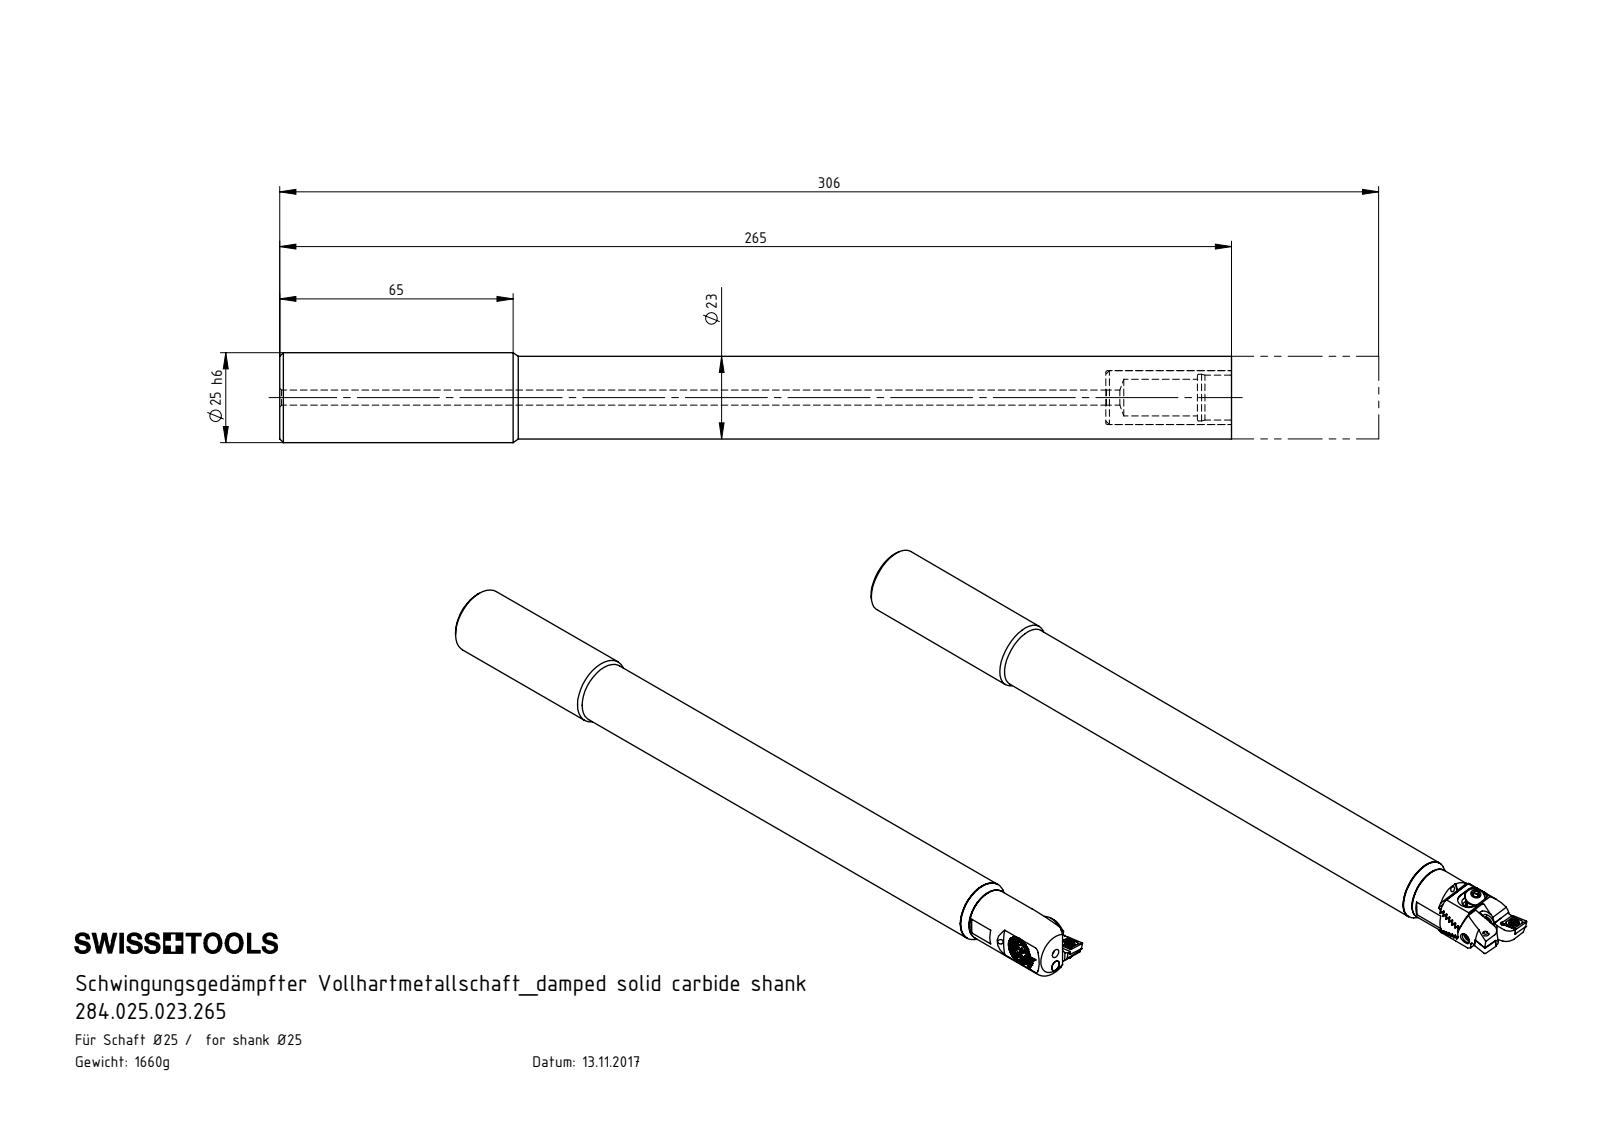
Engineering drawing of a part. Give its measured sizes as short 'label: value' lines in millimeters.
name: F20-ER1.101.006_A; F20-BG2.011.004_A; F20-WCA.001.005; F20-BG2.011.003_A (+8 more)
written by: SolidWorks 2017 (CONFIG_CONTROL_DESIGN)
unit: mm
bodies: 19 solids, 831 faces (344 planar, 166 cylindrical, 321 other)
size: 306 × 25 × 25
volume: 121 909 mm³; area: 38 219 mm²
holes: 4× ⌀2, 3× ⌀3.3, 1× ⌀1.6, 1× ⌀1.9, 1× ⌀2.05, 1× ⌀2.5, 1× ⌀2.8, 1× ⌀3, 1× ⌀3.85, 1× ⌀4, 1× ⌀4.2, 1× ⌀4.5
bosses: 2× ⌀4, 2× ⌀3.95, 1× ⌀25, 1× ⌀23, 1× ⌀20, 1× ⌀12, 1× ⌀10.98, 1× ⌀10.85
rounds: 6× R0.21, 5× R0.36, 2× R0.3, 2× R0.5, 2× R2, 2× R3, 2× R5, 1× R0.36
face distances: 265, 3, 268, 38, 230, 35, 6, 303.5, 73.5, 38.5
hole spacings: 5.6, 7, 12.6, 14
